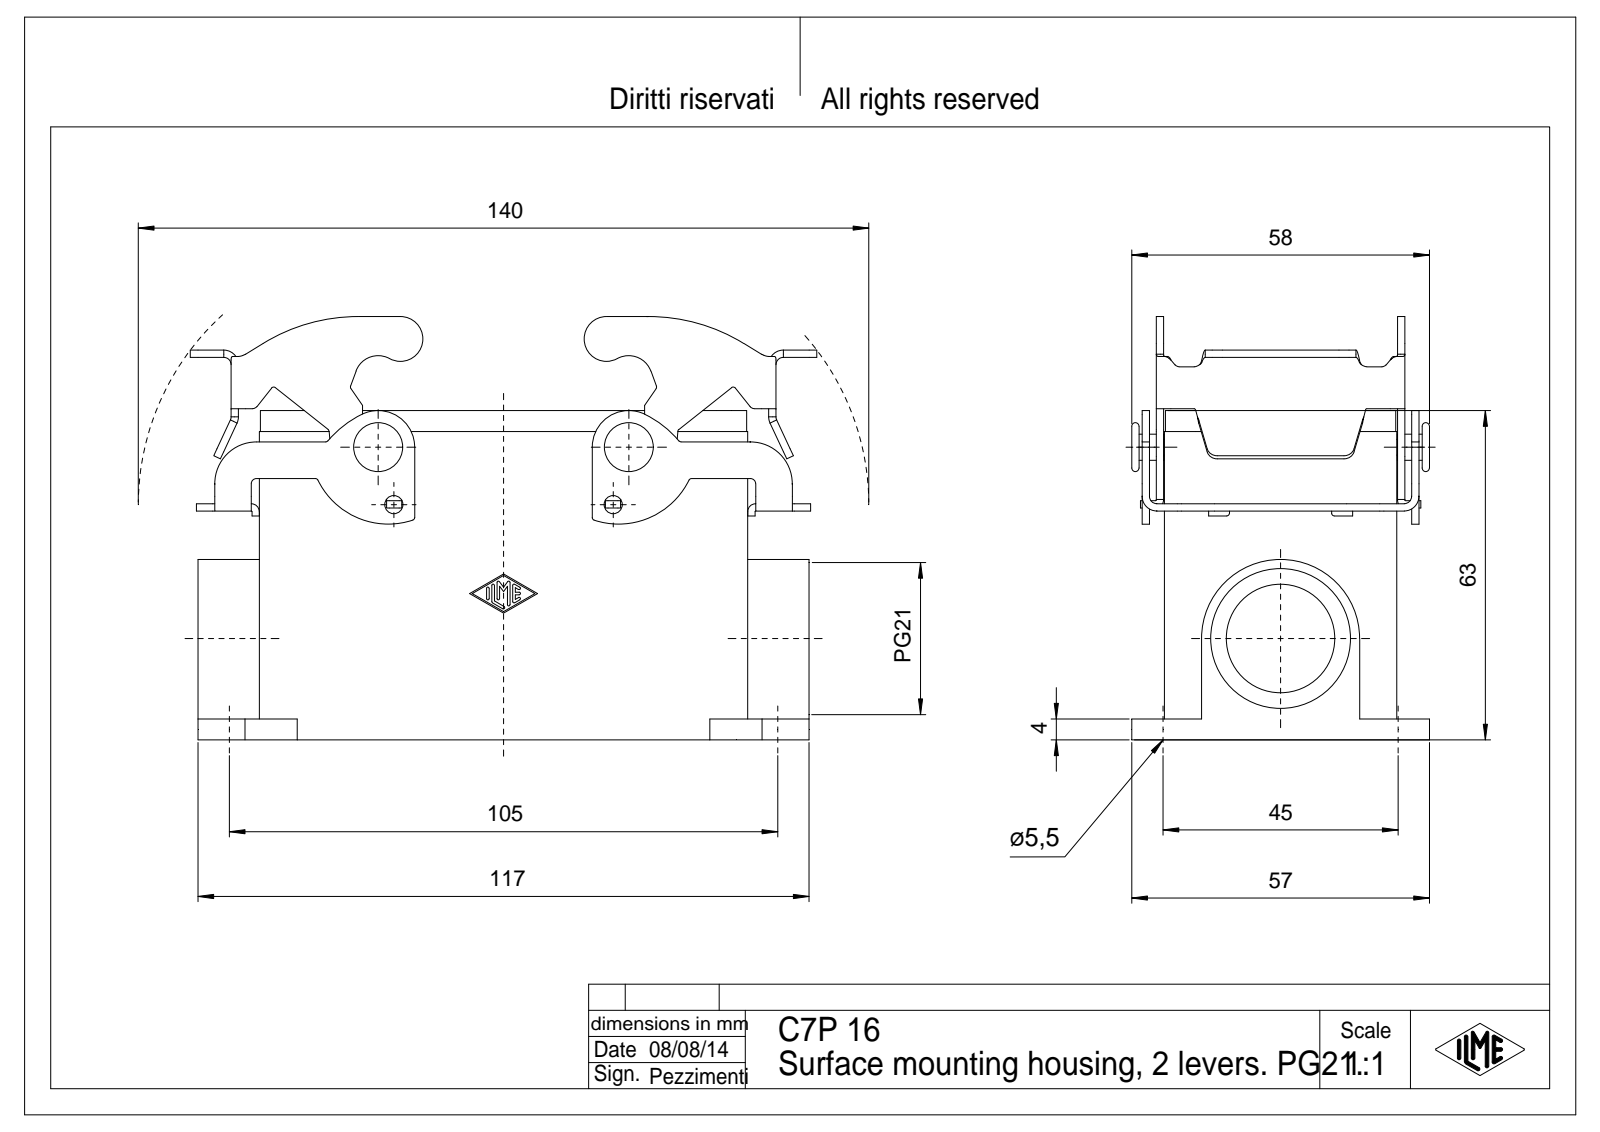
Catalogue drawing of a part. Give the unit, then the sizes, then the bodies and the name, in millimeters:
Units: millimetres
Overall size (bounding box): 119.97 × 81 × 57
Round holes (diameter × count): ⌀2.46 ×4, ⌀3 ×4, ⌀5.5 ×4, ⌀3.5 ×2, ⌀20.78 ×1, ⌀26.78 ×1
Round bosses / shafts (diameter × count): ⌀5 ×2, ⌀3.2 ×2, ⌀3 ×2
Partial cylindrical surfaces — rounded edges, fillets, slot ends (radius × count): R0.5 ×22, R1 ×18, R0.25 ×16, R1.5 ×14, R2 ×12, R1.4 ×10, R2.8 ×10, R8 ×6
Main face-to-face distances: 4, 40.5, 1.4, 44.5, 36.5, 2.7, 48.9, 1.55, 5.55, 42.05
Hole centre spacings: 16.43, 38.54, 91.69, 98.09, 27, 45, 77.5, 82.07
Volume: 111 426 mm³ · Surface area: 62 738 mm²
Bodies: 3 solids, 609 faces (293 planar, 272 cylindrical, 44 other)
Part name (STEP PRODUCT): p1; p2; p3; JCVP_16 (+1 more)
STEP written by: Creo Elements/Direct Modeling 18.0B 02-Dec-2011 (C) Parametric Technology GmbH (AUTOMOTIVE_DESIGN)
